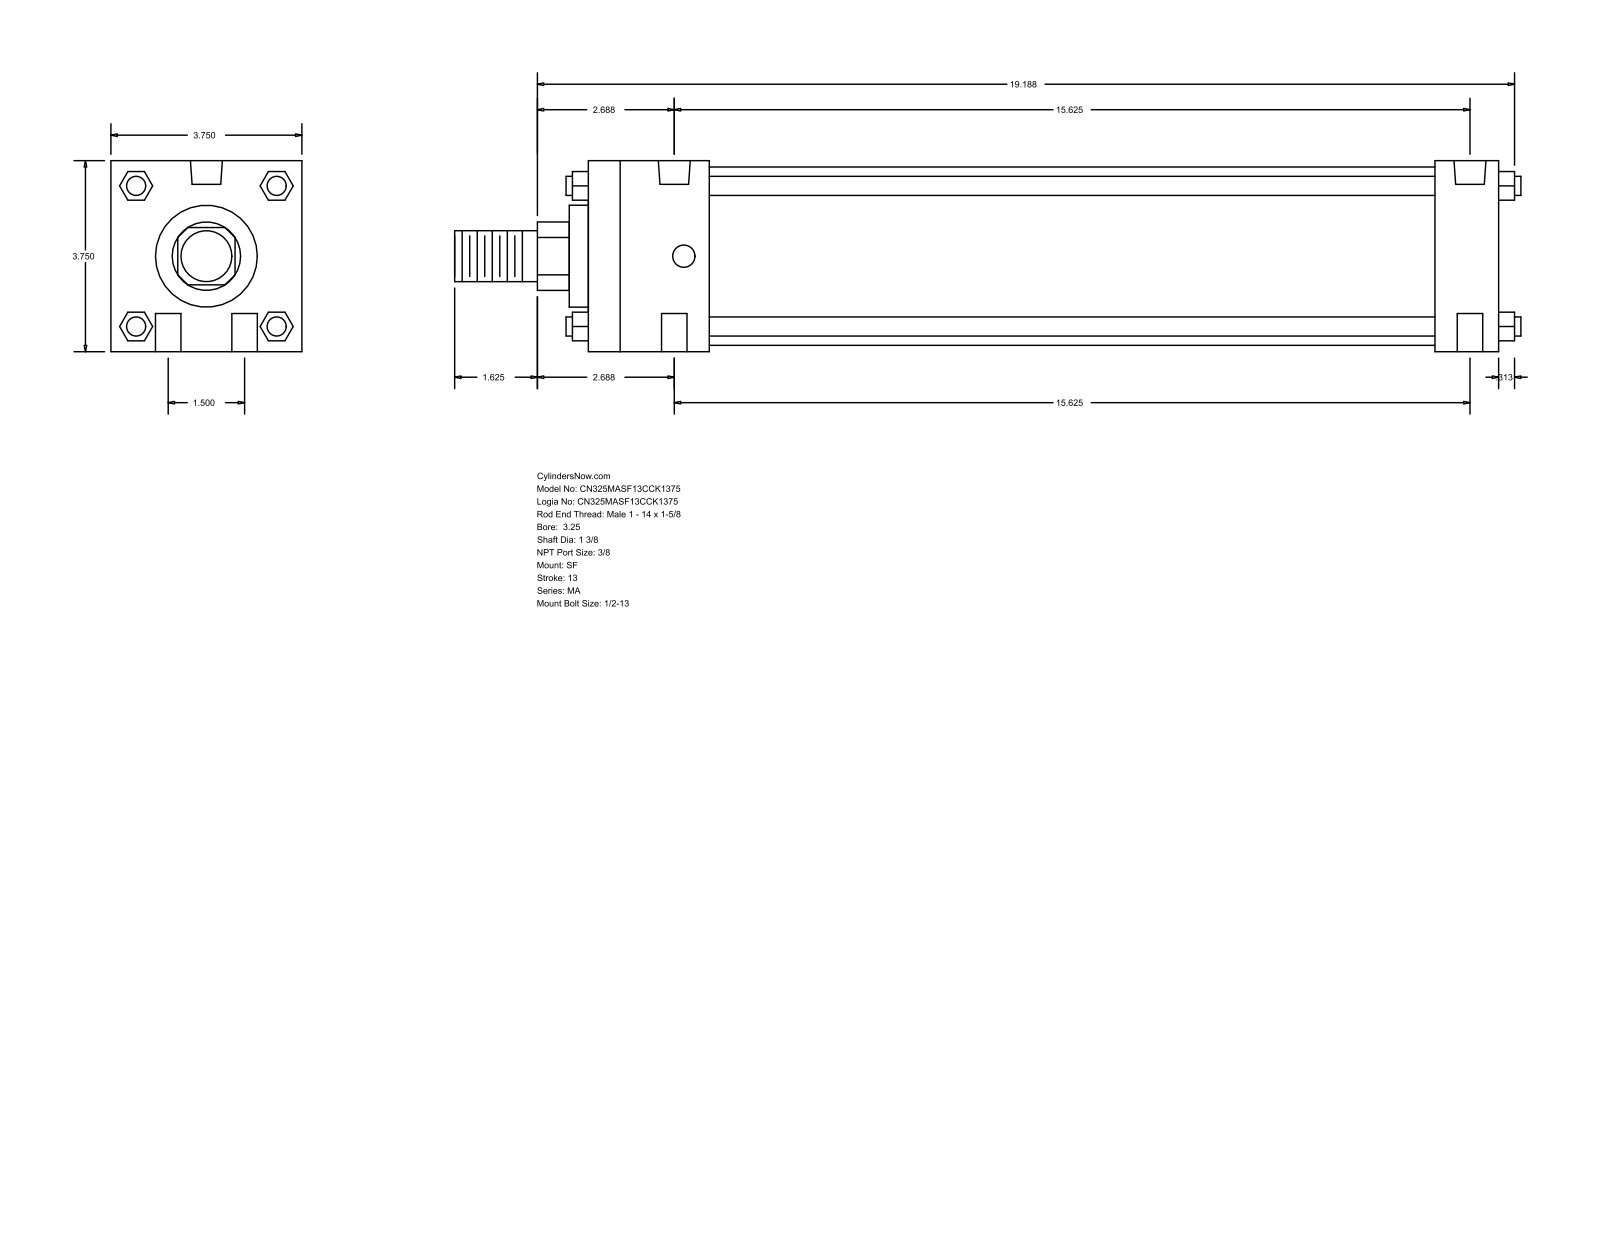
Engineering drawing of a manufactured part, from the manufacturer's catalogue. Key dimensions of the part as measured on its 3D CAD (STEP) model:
Part name (STEP PRODUCT): MA_SF__0325_1.375
STEP written by: GSSL Pune (CONFIG_CONTROL_DESIGN)
Units: millimetres
Bodies: 0 solids, 124 faces (94 planar, 30 cylindrical, 0 other)
Overall size (bounding box): 531.81 × 95.25 × 95.25
Round holes (diameter × count): ⌀12.7 ×4, ⌀11.11 ×2, ⌀15.93 ×2
Round bosses / shafts (diameter × count): ⌀9.53 ×4, ⌀88.9 ×1, ⌀50.8 ×1, ⌀34.92 ×1, ⌀25.4 ×1
Partial cylindrical surfaces — rounded edges, fillets, slot ends (radius × count): R17.06 ×1
Main face-to-face distances: 95.24, 454.03, 422.28, 31.75, 60.32, 361.96, 393.71, 9.52, 69.84, 431.8
Hole centre spacings: 19.05, 397.34, 396.88, 38.1, 398.7, 387.35
